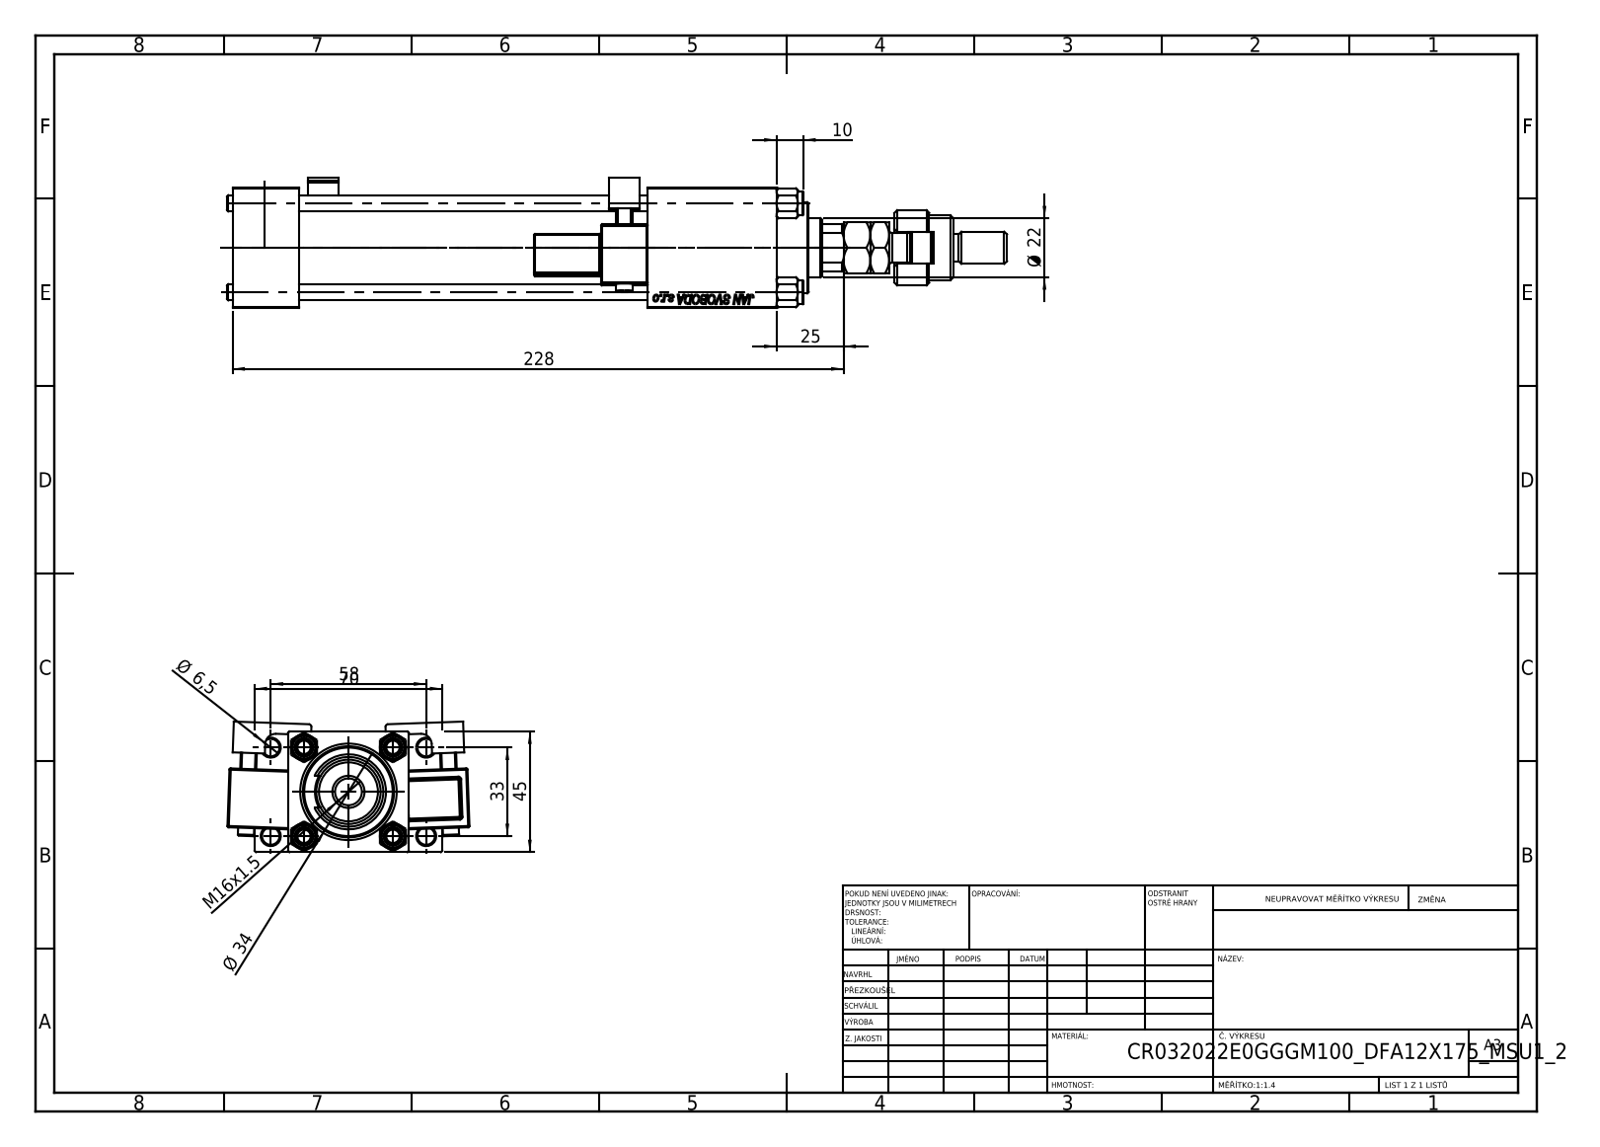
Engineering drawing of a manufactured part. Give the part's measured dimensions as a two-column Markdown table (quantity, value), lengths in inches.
| quantity | value |
| --- | --- |
| part name | MFA; V215CR_TYCINKA_E; V215CR_E_Body; V215_VC_A (+4 more) |
| STEP written by | SolidWorks 2019 (CONFIG_CONTROL_DESIGN) |
| units | inches |
| bodies | 15 solids, 1379 faces (587 planar, 160 cylindrical, 632 other) |
| overall size | 11.457 × 3.556 × 1.918 |
| volume | 22.02 in³ |
| surface area | 199.7 in² |
| round holes (diameter × count) | 0.236 × 4, 0.256 × 4, 0.276 × 2, 0.518 × 2, 0.787 × 2, 0.413 × 1, 0.866 × 1, 0.945 × 1, 0.984 × 1, 1.26 × 1, 1.299 × 1 |
| round bosses / shafts (diameter × count) | 0.354 × 4, 0.236 × 2, 1.496 × 1, 1.339 × 1, 1.102 × 1, 0.709 × 1, 0.472 × 1, 0.433 × 1 |
| partial cylindrical surfaces (radius × count) | 0.02 × 48, 0.039 × 2, 0.098 × 2, 0.157 × 2, 0.384 × 1, 0.413 × 1 |
| main face-to-face distances | 1.772, 0.984, 0.492, 0.118, 2.264, 6.102, 5.118, 7.992, 2.756, 0.905 |
| hole center spacings | 0.488, 0.924, 1.307, 1.314, 1.392, 1.795, 2.219, 1.299 |
